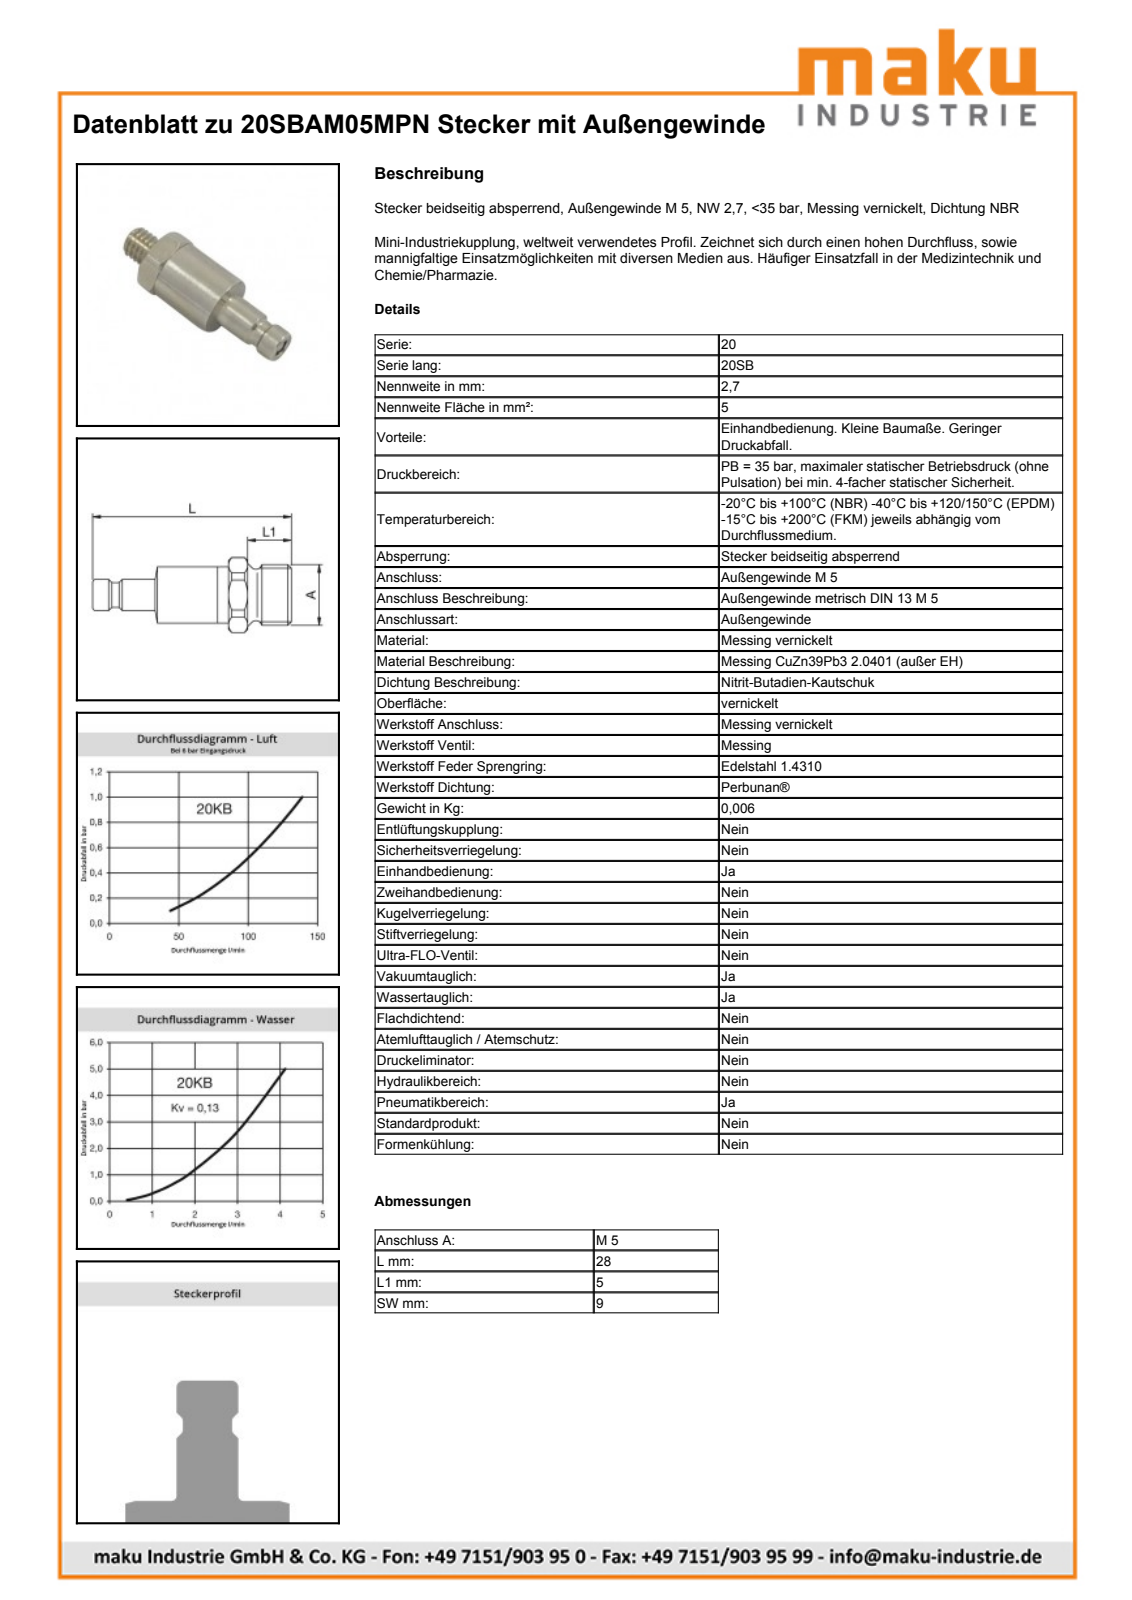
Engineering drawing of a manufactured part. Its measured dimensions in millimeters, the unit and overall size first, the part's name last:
Units: millimetres
Overall size (bounding box): 28.05 × 9.79 × 9.72
Round holes (diameter × count): ⌀6.3 ×1, ⌀8 ×1, ⌀8.1 ×1
Round bosses / shafts (diameter × count): ⌀9 ×1, ⌀7.3 ×1, ⌀6.8 ×1, ⌀6.29 ×1, ⌀5 ×1, ⌀3.95 ×1
Partial cylindrical surfaces — rounded edges, fillets, slot ends (radius × count): R4.95 ×1
Main face-to-face distances: 9, 3.05, 20, 23.05, 28.05, 8.05, 5, 15.55, 4.45, 7.5
Volume: 1 085 mm³ · Surface area: 1 010 mm²
Bodies: 1 solid, 58 faces (12 planar, 18 cylindrical, 28 other)
Part name (STEP PRODUCT): D105898
STEP written by: Autodesk Inventor 2011 (AUTOMOTIVE_DESIGN)
